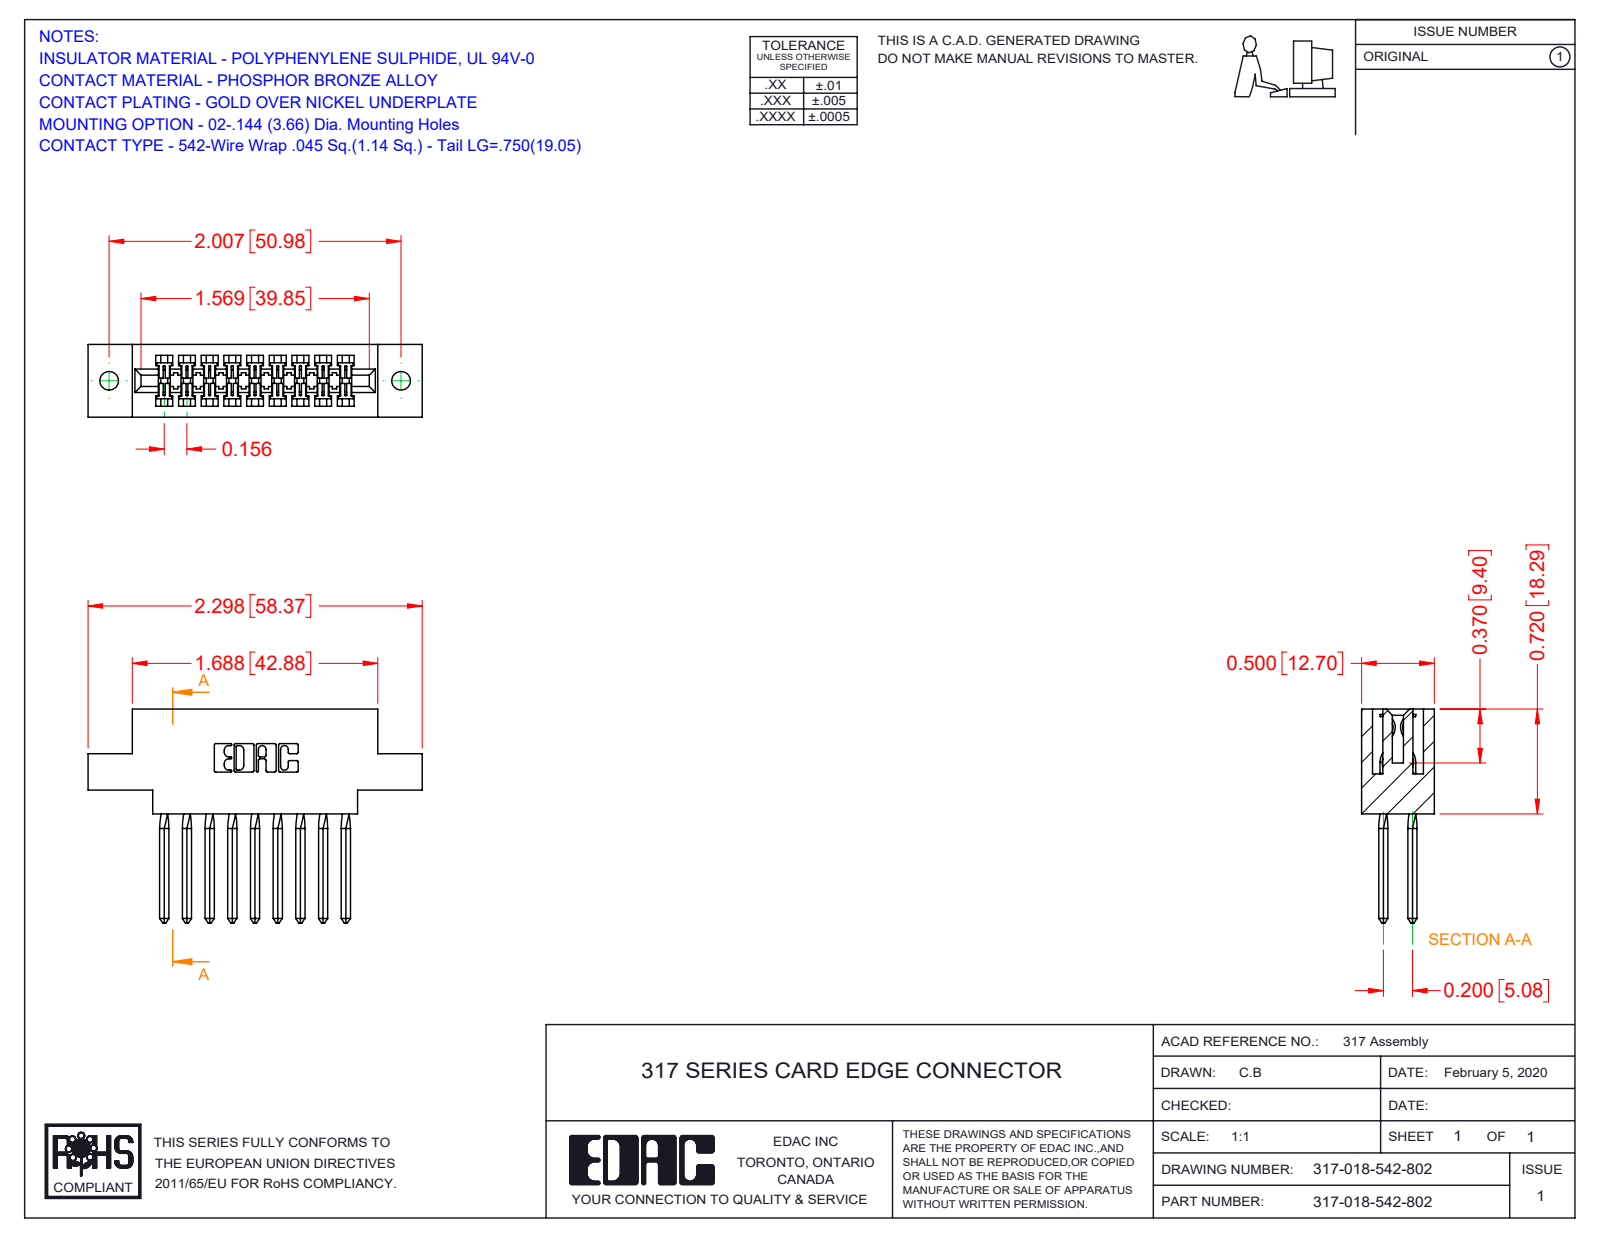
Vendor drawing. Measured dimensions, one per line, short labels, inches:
name: 317 Part_.144 Dia; 317-018-542-802; 317-290-003_542
written by: SolidWorks 2016 (CONFIG_CONTROL_DESIGN)
unit: in
bodies: 19 solids, 1128 faces (886 planar, 170 cylindrical, 72 other)
size: 2.298 × 1.47 × 0.5
volume: 0.517 in³; area: 16.22 in²
holes: 2× ⌀0.128
rounds: 36× R0.006, 22× R0.01, 6× R0.007, 6× R0.031, 3× R0.026, 2× R0.074, 2× R0.089, 2× R0.1
face distances: 0.5, 0.075, 0.425, 0.11, 0.116, 0.22, 0.156, 0.35, 0.136, 0.2
hole spacings: 2.007
